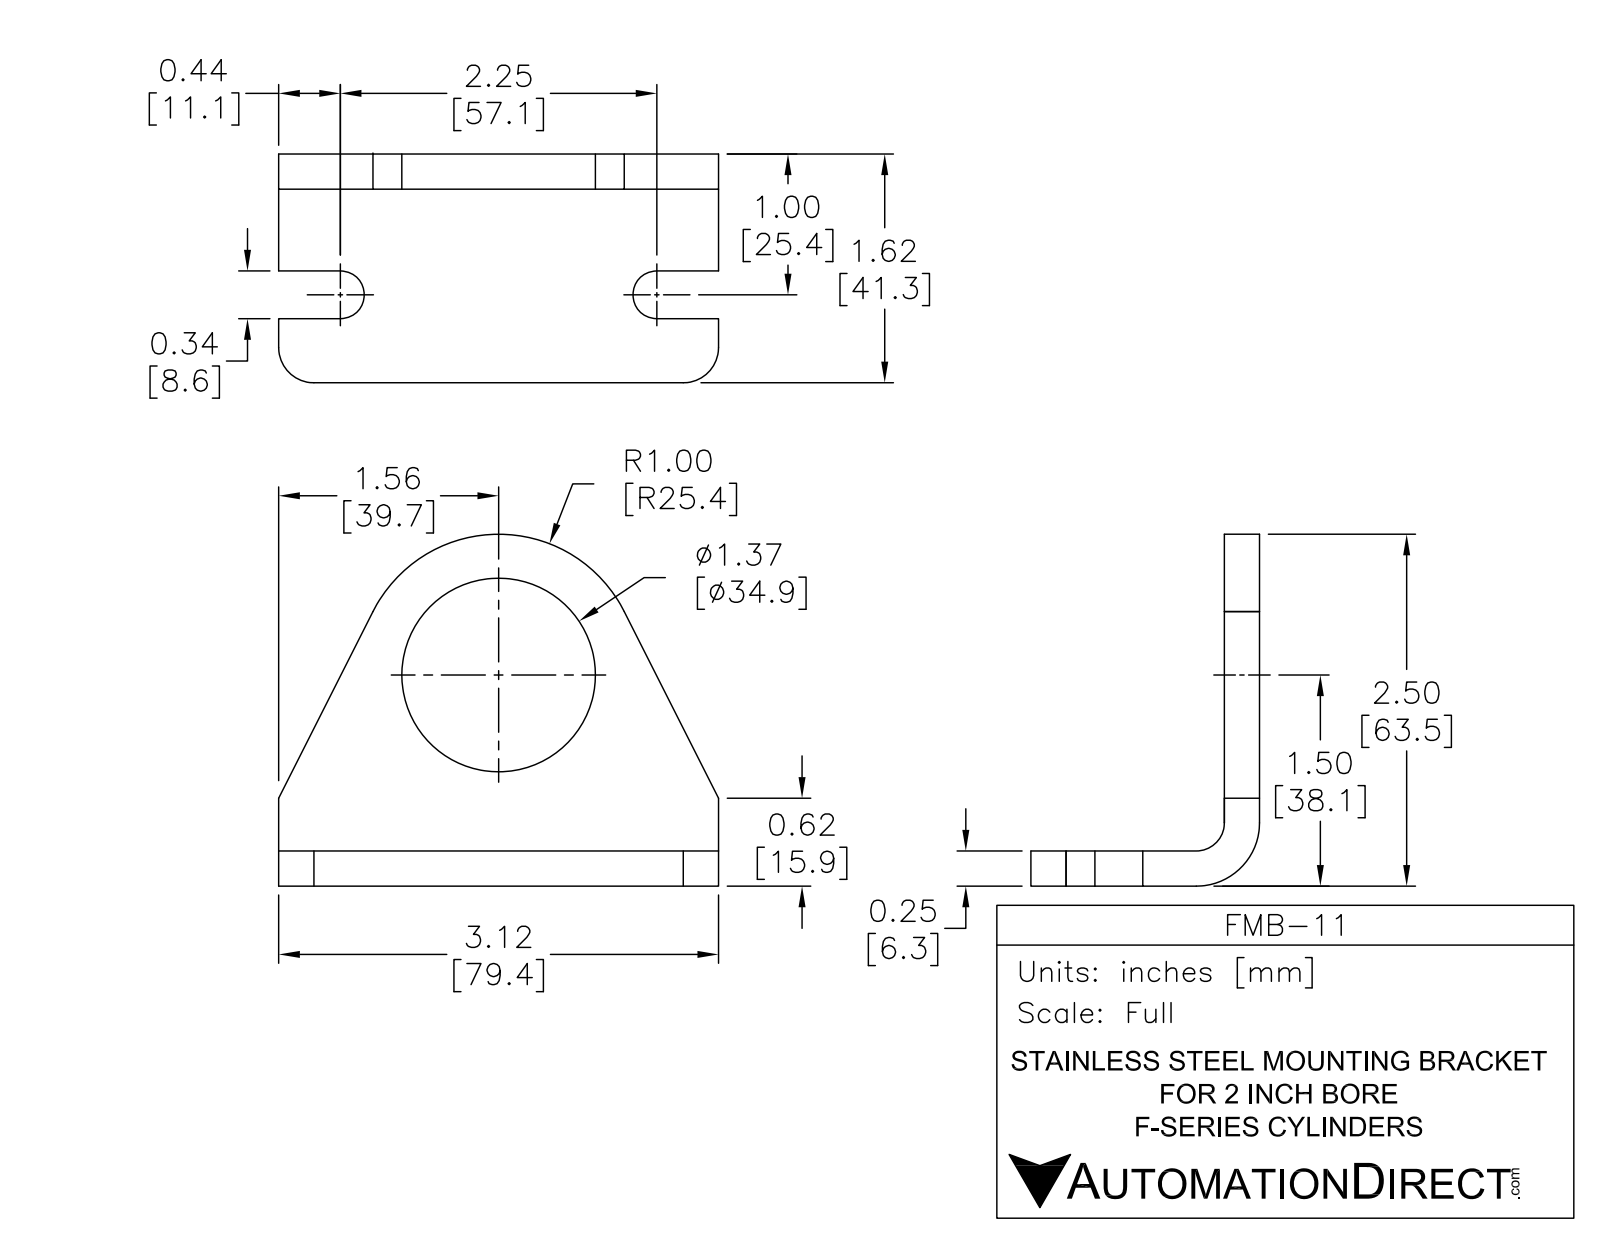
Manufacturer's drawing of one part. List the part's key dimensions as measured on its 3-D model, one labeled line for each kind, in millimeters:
Part name (STEP PRODUCT): FMB-11
STEP written by: SolidWorks 2017 (AUTOMOTIVE_DESIGN)
Units: millimetres
Bodies: 1 solid, 28 faces (19 planar, 9 cylindrical, 0 other)
Overall size (bounding box): 79.4 × 63.5 × 41.3
Volume: 32 810 mm³ · Surface area: 13 270 mm²
Round holes (diameter × count): ⌀34.9 ×1
Partial cylindrical surfaces — rounded edges, fillets, slot ends (radius × count): R4.3 ×2, R11.1 ×2, R1.5 ×1, R7.9 ×1, R25.4 ×1
Main face-to-face distances: 6.4, 34.9, 41.3, 79.4, 11.6, 23.3, 29.7, 20.2, 8.6, 14.8
